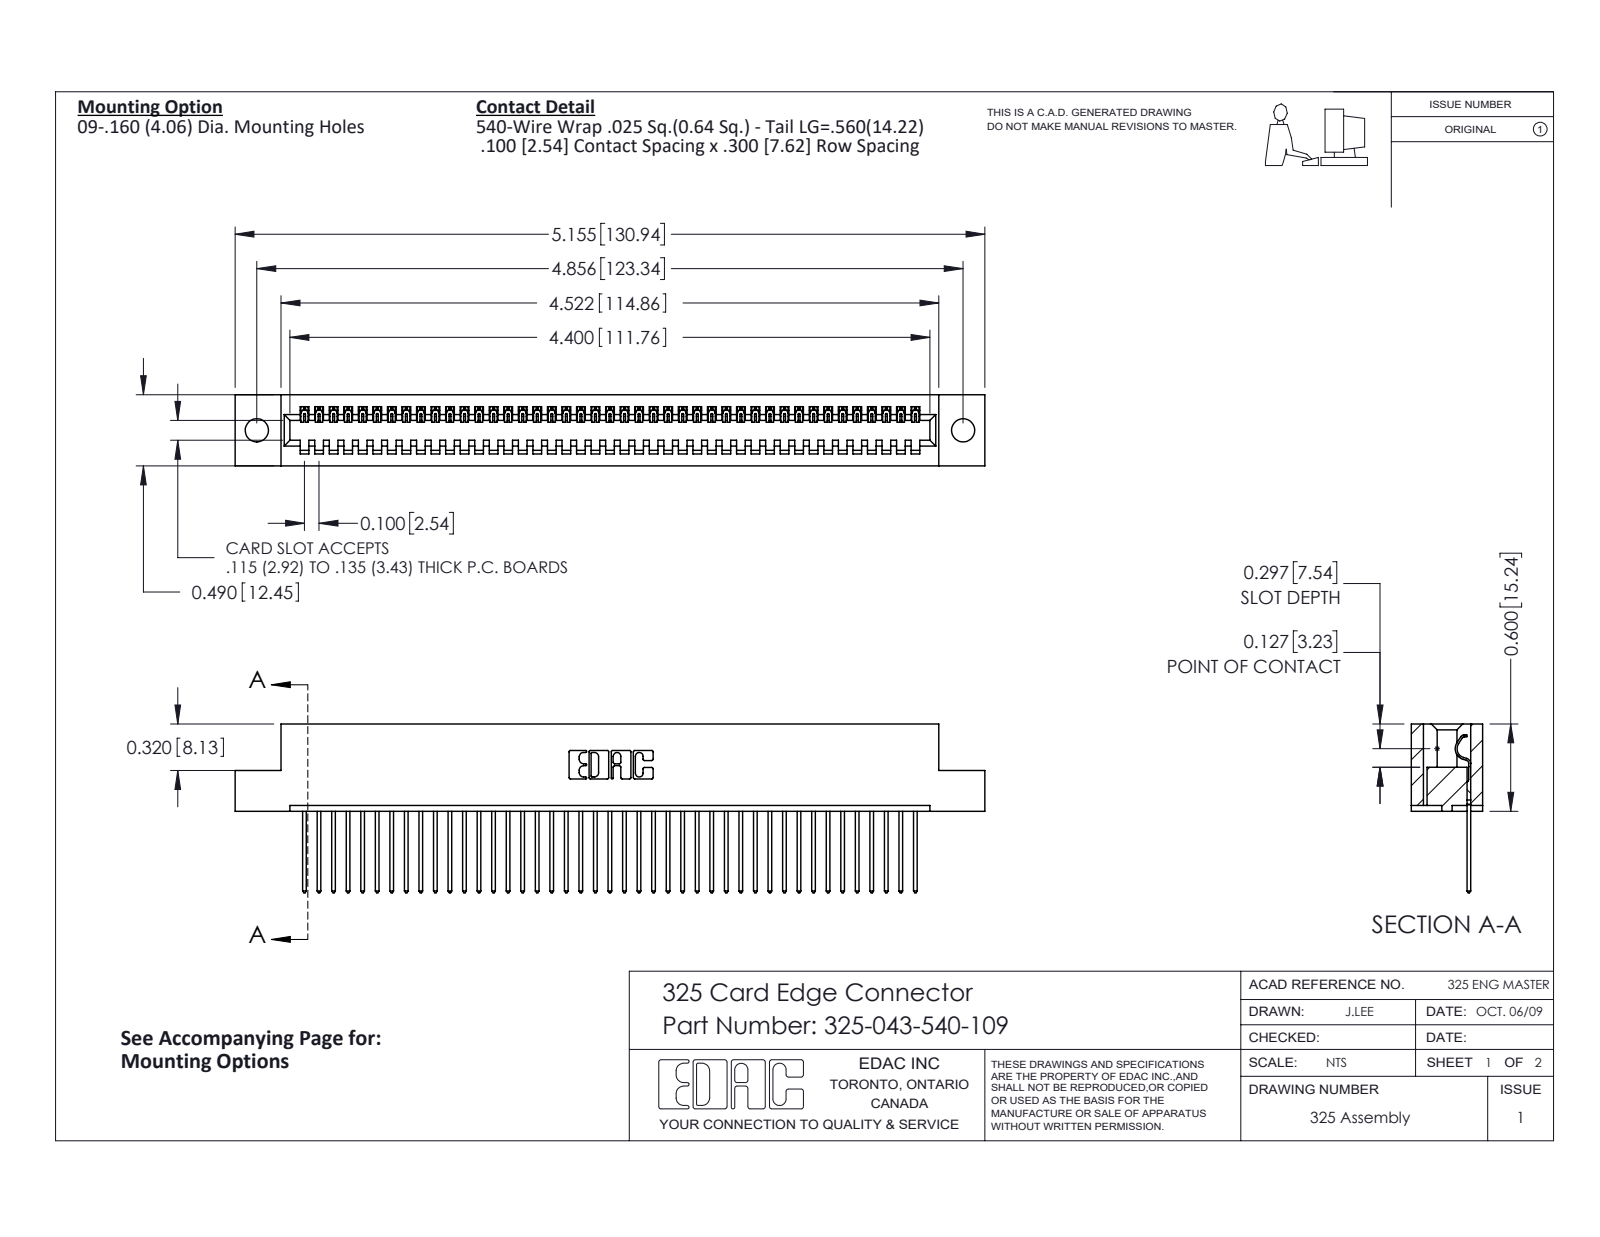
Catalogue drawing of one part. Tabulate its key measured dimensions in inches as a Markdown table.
| quantity | value |
| --- | --- |
| part name | 325-292-001_325-293-140; 325-043-540-109; 325 Part_.160 TH |
| STEP written by | SolidWorks 2016 (CONFIG_CONTROL_DESIGN) |
| units | inches |
| bodies | 44 solids, 2608 faces (1876 planar, 732 cylindrical, 0 other) |
| overall size | 5.155 × 1.16 × 0.49 |
| volume | 1.004 in³ |
| surface area | 28.4 in² |
| round holes (diameter × count) | 0.16 × 2 |
| partial cylindrical surfaces (radius × count) | 0.006 × 86, 0.01 × 86, 0.01 × 22, 0.007 × 6, 0.031 × 6, 0.026 × 3, 0.014 × 1, 0.022 × 1 |
| main face-to-face distances | 0.083, 0.407, 0.49, 0.3, 0.107, 0.383, 0.025, 0.325, 0.56, 0.04 |
| hole center spacings | 4.856 |
